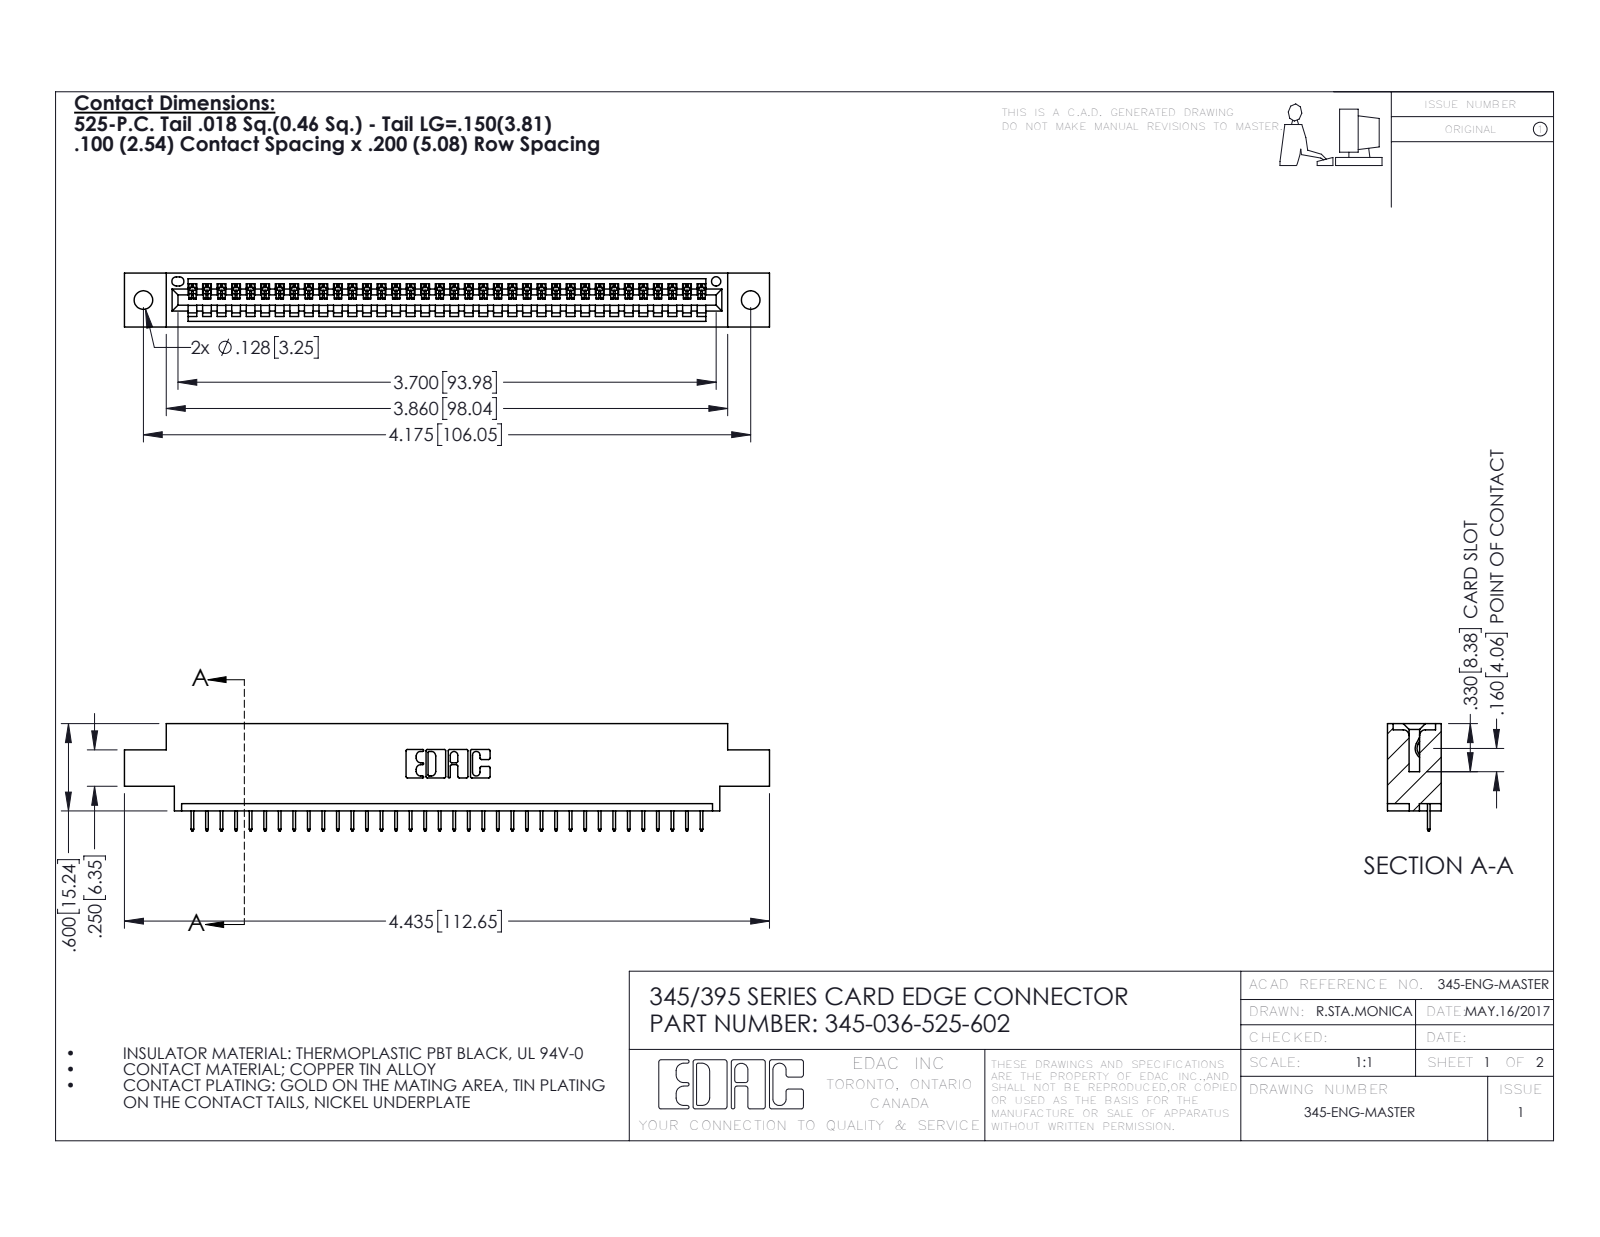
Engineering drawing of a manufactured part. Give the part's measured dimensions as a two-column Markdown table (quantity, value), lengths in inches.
| quantity | value |
| --- | --- |
| part name | 345-292-001_345-293-125; 345-036-525-602; 345 Part_0.170 Offset - 0.128 Dia |
| STEP written by | SolidWorks 2020 (CONFIG_CONTROL_DESIGN) |
| units | inches |
| bodies | 37 solids, 2362 faces (1740 planar, 622 cylindrical, 0 other) |
| overall size | 4.435 × 0.737 × 0.37 |
| volume | 0.632 in³ |
| surface area | 20.22 in² |
| round holes (diameter × count) | 0.128 × 2, 0.064 × 1 |
| partial cylindrical surfaces (radius × count) | 0.006 × 72, 0.01 × 22, 0.007 × 6, 0.031 × 6, 0.026 × 3, 0.031 × 2, 0.04 × 2, 0.014 × 1 |
| main face-to-face distances | 0.072, 0.298, 0.37, 0.2, 0.098, 0.272, 0.025, 0.225, 0.175, 0.072 |
| hole center spacings | 0.27, 3.939, 4.175 |
